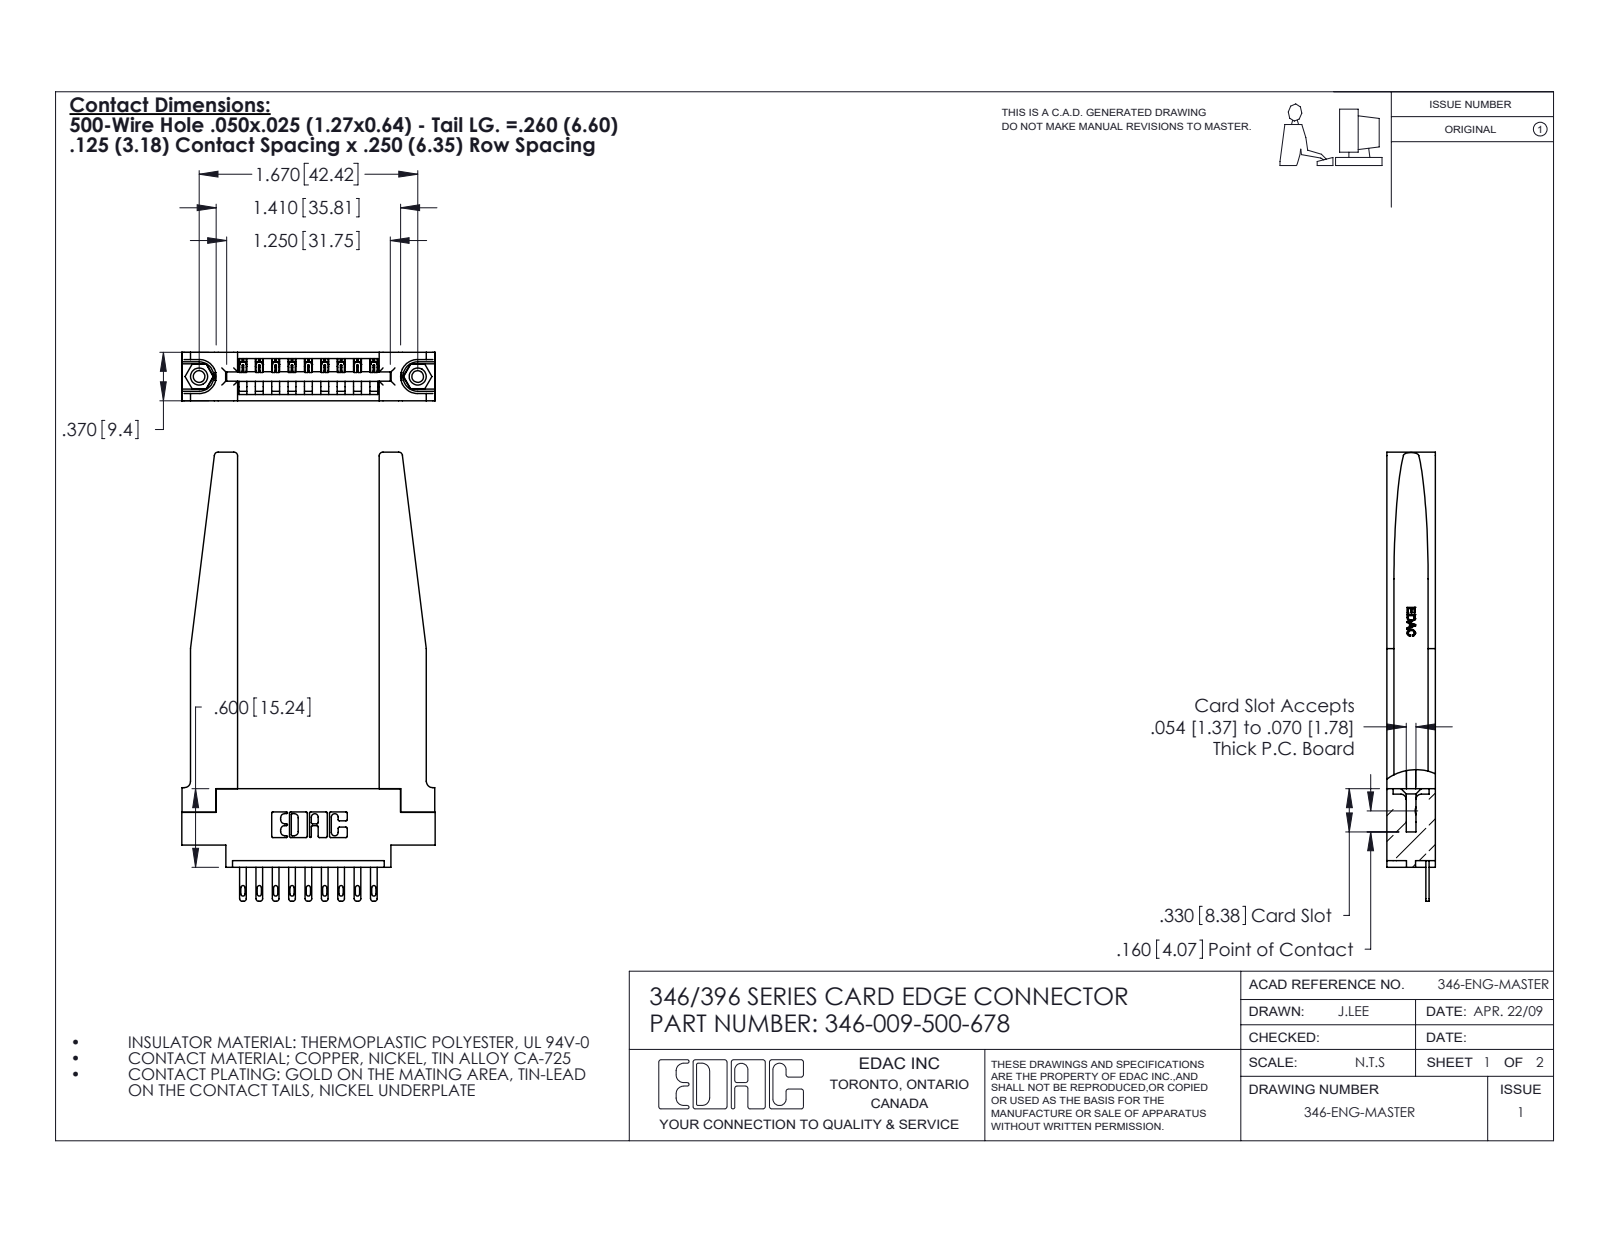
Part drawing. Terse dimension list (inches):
name: 345-250-001_345-250-001-102; 346-220-078_345-220-078; 345-292-001_345-293-100; 346 Part_0.170 Offset - 0.156 Dia-TH (+1 more)
written by: SolidWorks 2020 (CONFIG_CONTROL_DESIGN)
unit: in
bodies: 14 solids, 860 faces (542 planar, 266 cylindrical, 52 other)
size: 3.43 × 1.935 × 0.37
volume: 0.685 in³; area: 18.27 in²
holes: 2× ⌀0.089, 2× ⌀0.125, 2× ⌀0.156, 1× ⌀0.064
bosses: 2× ⌀0.155
rounds: 22× R0.01, 18× R0.006, 18× R0.016, 18× R0.02, 8× R0.03, 6× R0.007, 6× R0.031, 3× R0.026
face distances: 0.37, 0.15, 0.072, 0.148, 0.22, 0.048, 0.322, 0.25, 0.102, 0.173
hole spacings: 0.246, 1.465, 1.67
